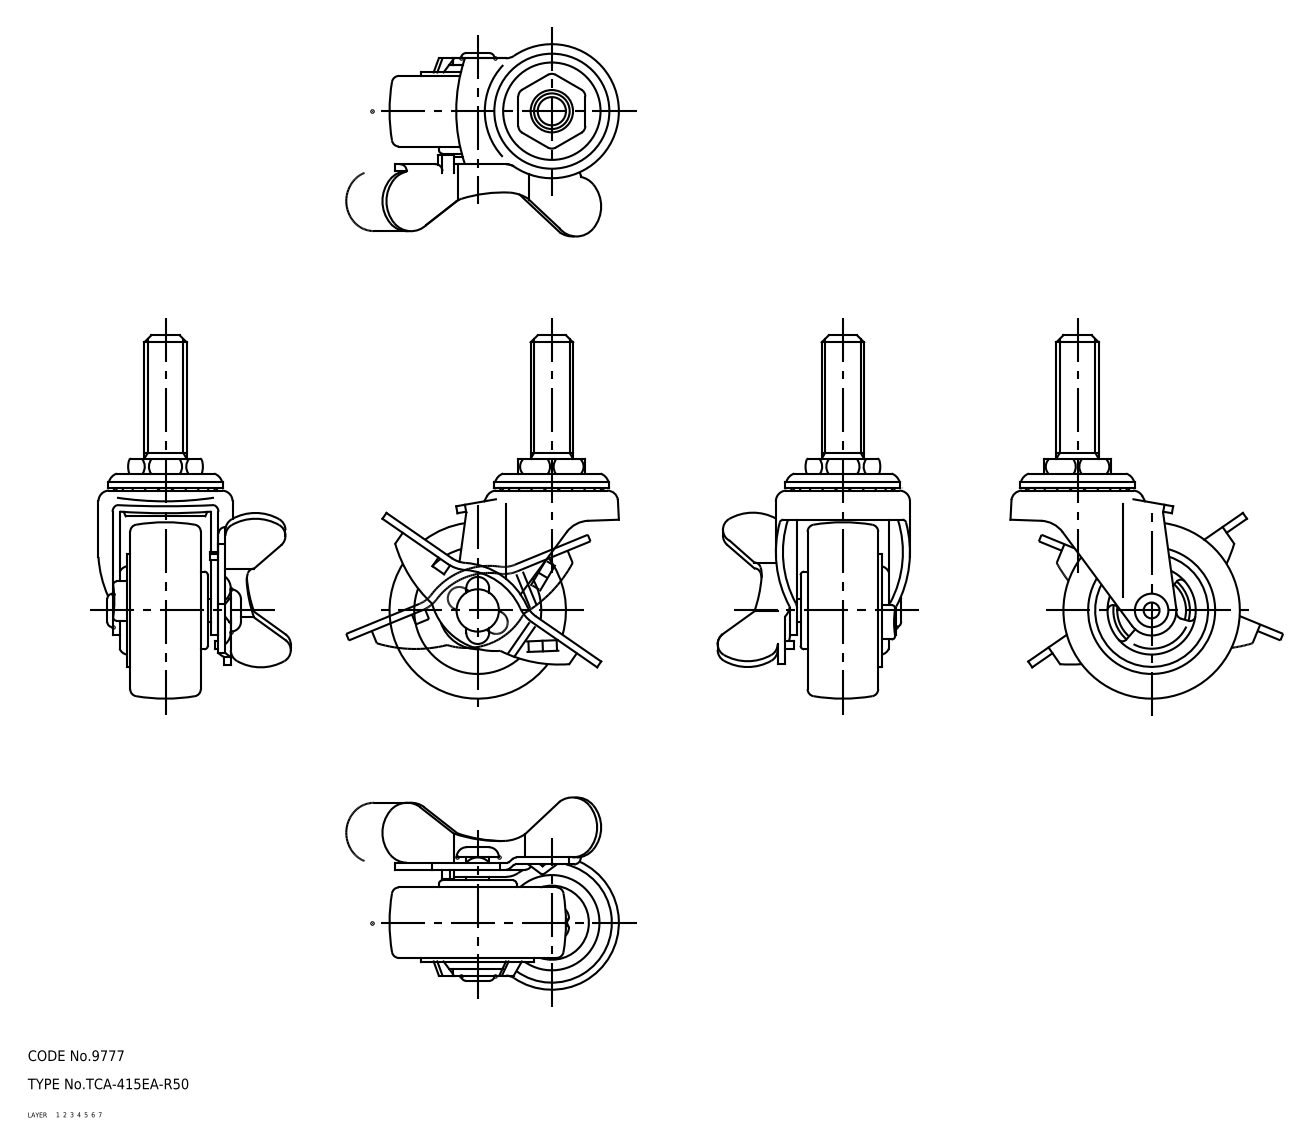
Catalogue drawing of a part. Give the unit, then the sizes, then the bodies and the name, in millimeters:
Units: millimetres
Overall size (bounding box): 103 × 67.42 × 54.5
Volume: 60 150 mm³ · Surface area: 25 627 mm²
Bodies: 6 solids, 312 faces (0 planar, 0 cylindrical, 312 other)
Part name (STEP PRODUCT): wheel; mounting plate; main shaft; lever (+2 more)
STEP written by: CADfix (AUTOMOTIVE_DESIGN)
